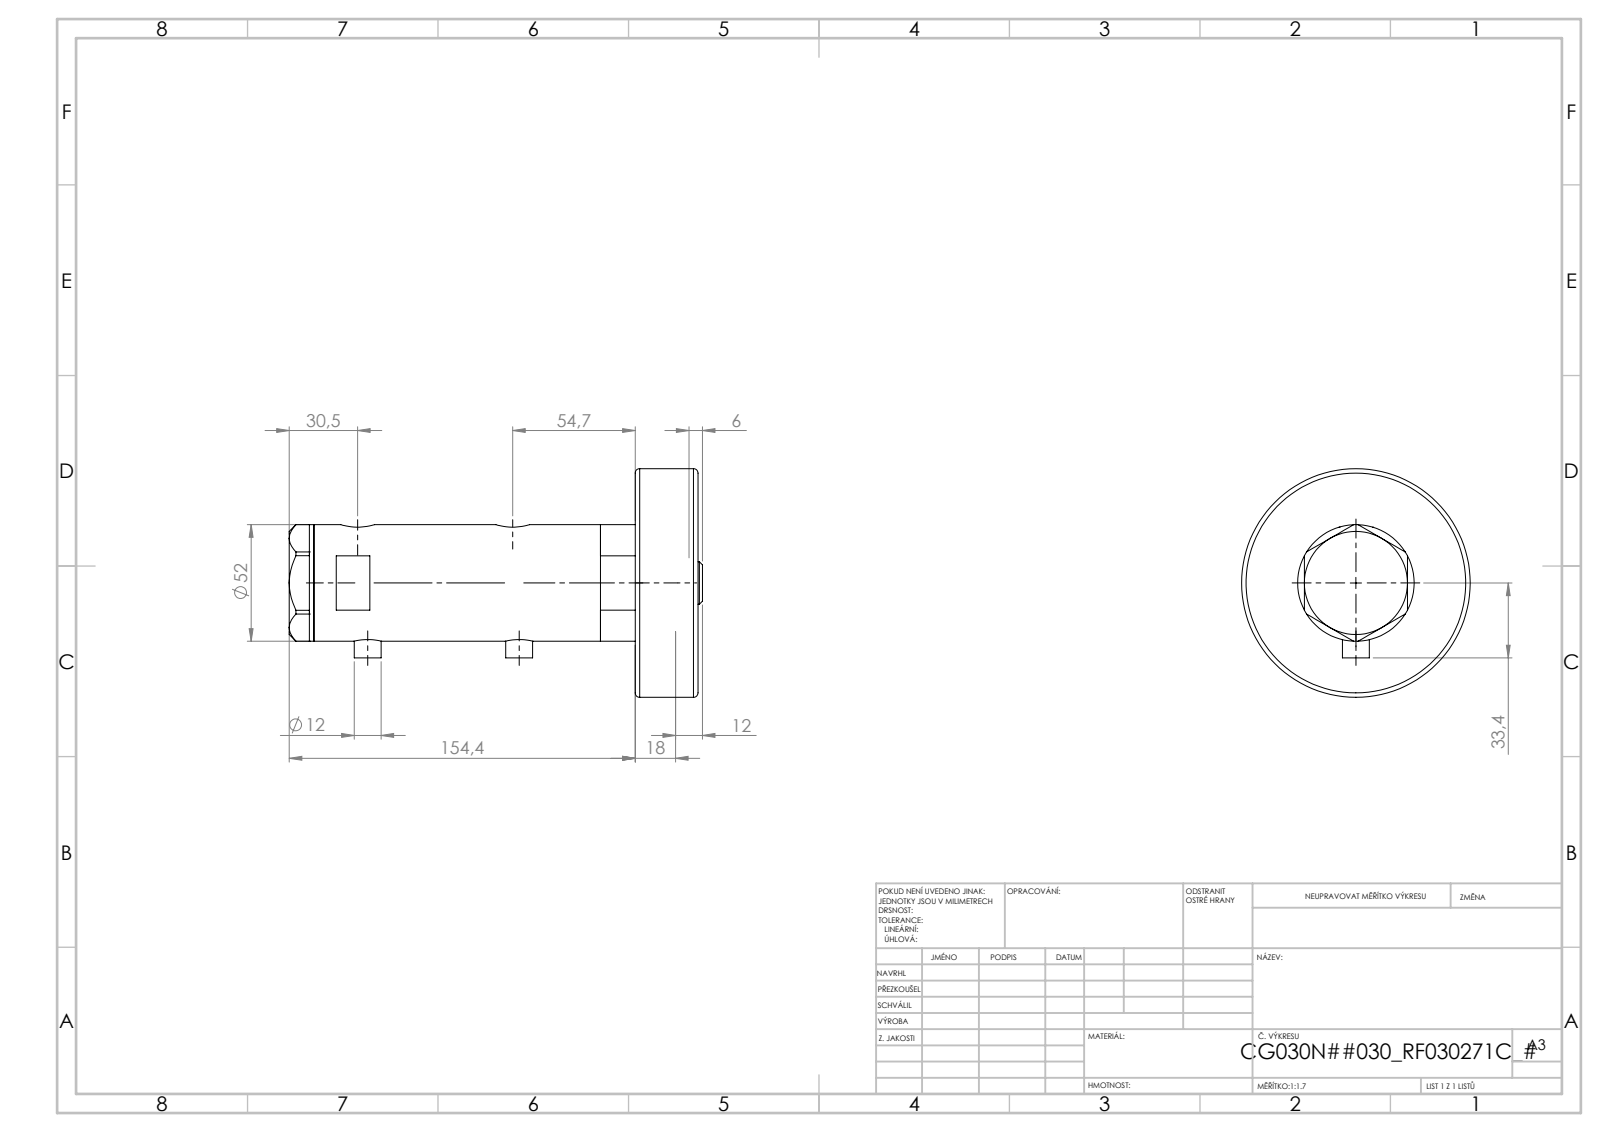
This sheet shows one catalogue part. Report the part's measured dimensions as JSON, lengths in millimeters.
{"part_name": "V270CG_271C; V270CG_VC; V270CG_MIDDLE; V270CG_FRONT (+1 more)", "step_written_by": "SolidWorks 2019 (CONFIG_CONTROL_DESIGN)", "units": "millimeters", "bodies": {"solids": 5, "faces": 150, "planar": 69, "cylindrical": 57, "other": 24}, "overall_size": [179.02, 102, 102], "volume_mm3": 512514, "surface_area_mm2": 100469, "round_holes": [[5, 2], [9.73, 2], [12.5, 2], [15, 2], [6.5, 1], [20, 1], [21.5, 1], [30, 1], [33, 1], [40, 1], [44, 1]], "round_bosses_or_shafts": [[12, 2], [102, 1], [52, 1], [38, 1], [19, 1]], "face_to_face_distances": [28, 135.45, 163.45, 23.81, 111.64, 139.64, 10.99, 34.8, 146.44, 174.44], "hole_center_spacings": [2.9, 4.5, 56.75, 59.65, 61.25, 64.15, 2.89, 2.91]}
